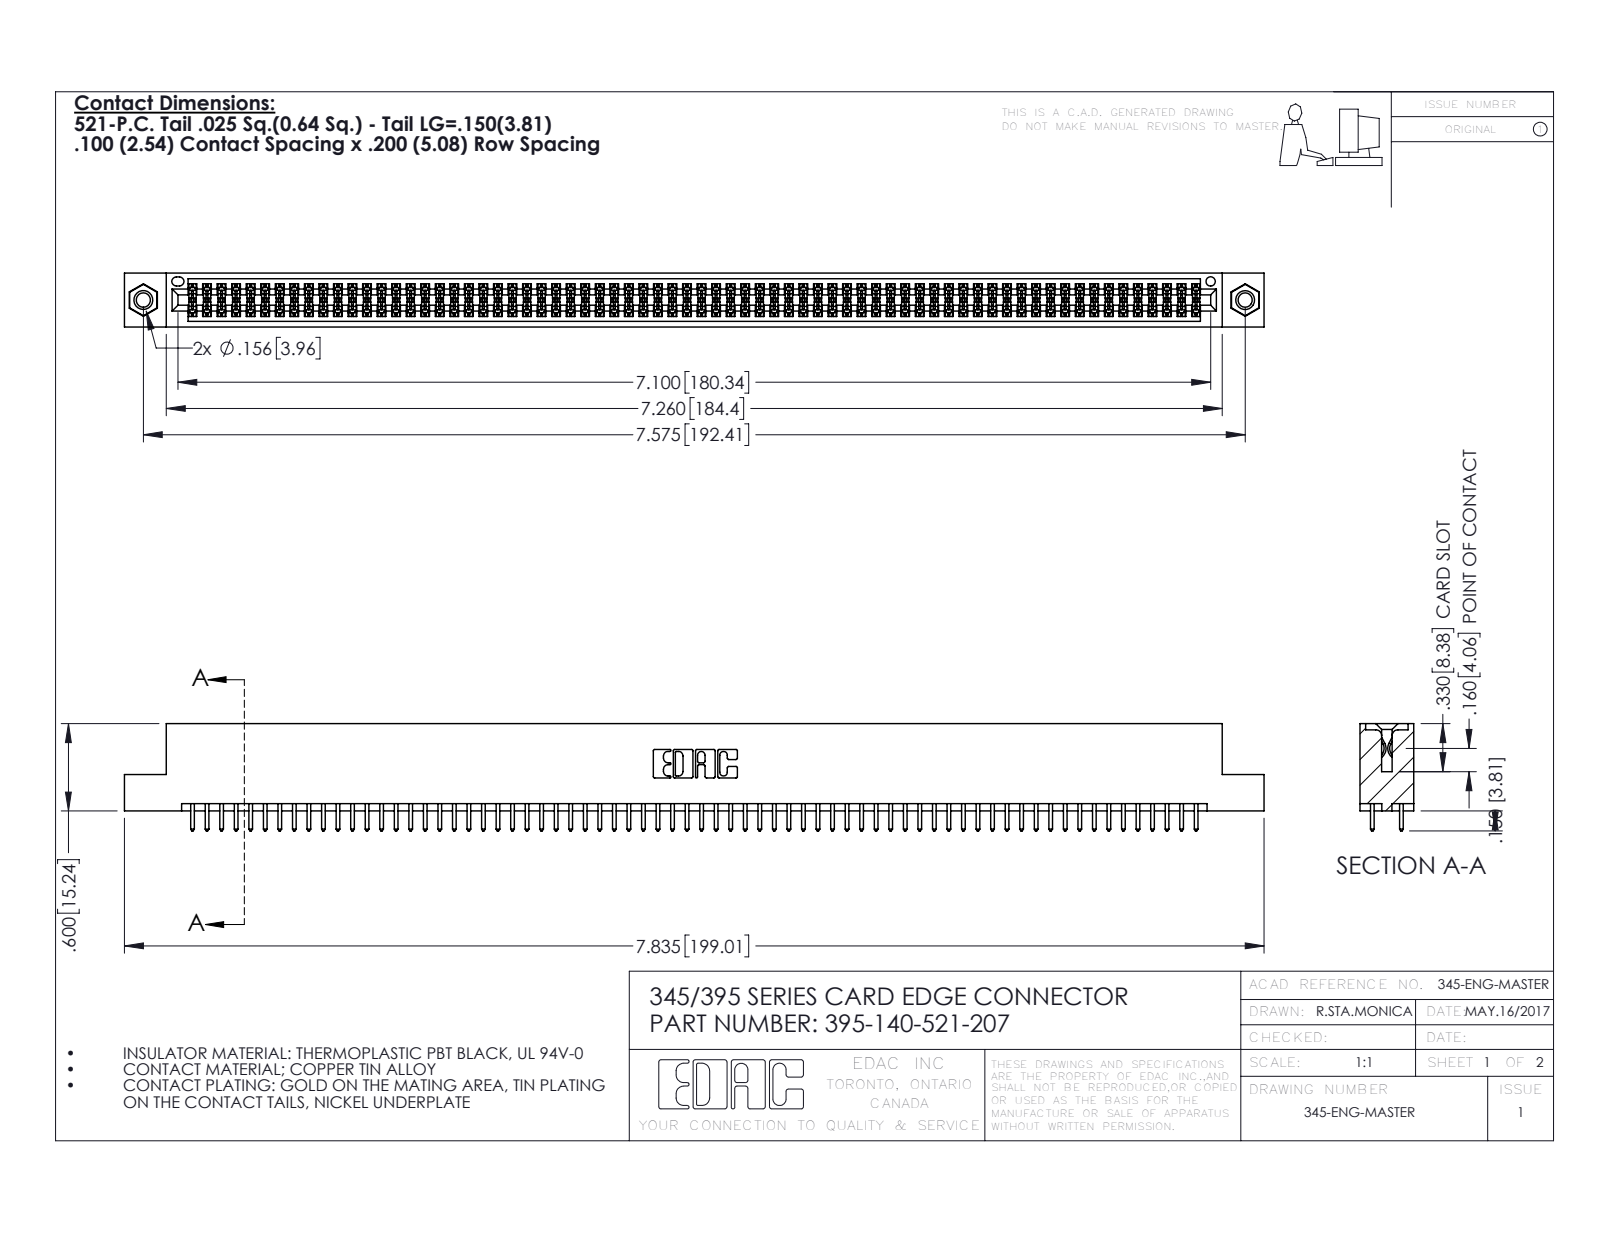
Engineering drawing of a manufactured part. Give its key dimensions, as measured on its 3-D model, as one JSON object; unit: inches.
{"part_name": "345-250-001_345-250-005-103; 395-140-521-207; 345 Part_Flush Mounting Lugs - 0.156 Dia-TI; 345-292-001_345-293-121", "step_written_by": "SolidWorks 2016 (CONFIG_CONTROL_DESIGN)", "units": "inches", "bodies": {"solids": 143, "faces": 7186, "planar": 4732, "cylindrical": 2438, "other": 16}, "overall_size": [7.835, 0.737, 0.37], "volume_in3": 1.191, "surface_area_in2": 45.03, "round_holes": [[0.098, 2], [0.125, 2], [0.156, 2], [0.064, 1]], "round_bosses_or_shafts": [[0.155, 2]], "partial_cylinders_radius": [[0.006, 210], [0.01, 140], [0.01, 22], [0.007, 6], [0.031, 6], [0.026, 3], [0.014, 2], [0.019, 2]], "face_to_face_distances": [0.072, 0.298, 0.2, 0.098, 0.272, 0.025, 0.37, 0.225, 0.175, 0.149], "hole_center_spacings": [0.27, 7.339, 7.575]}
